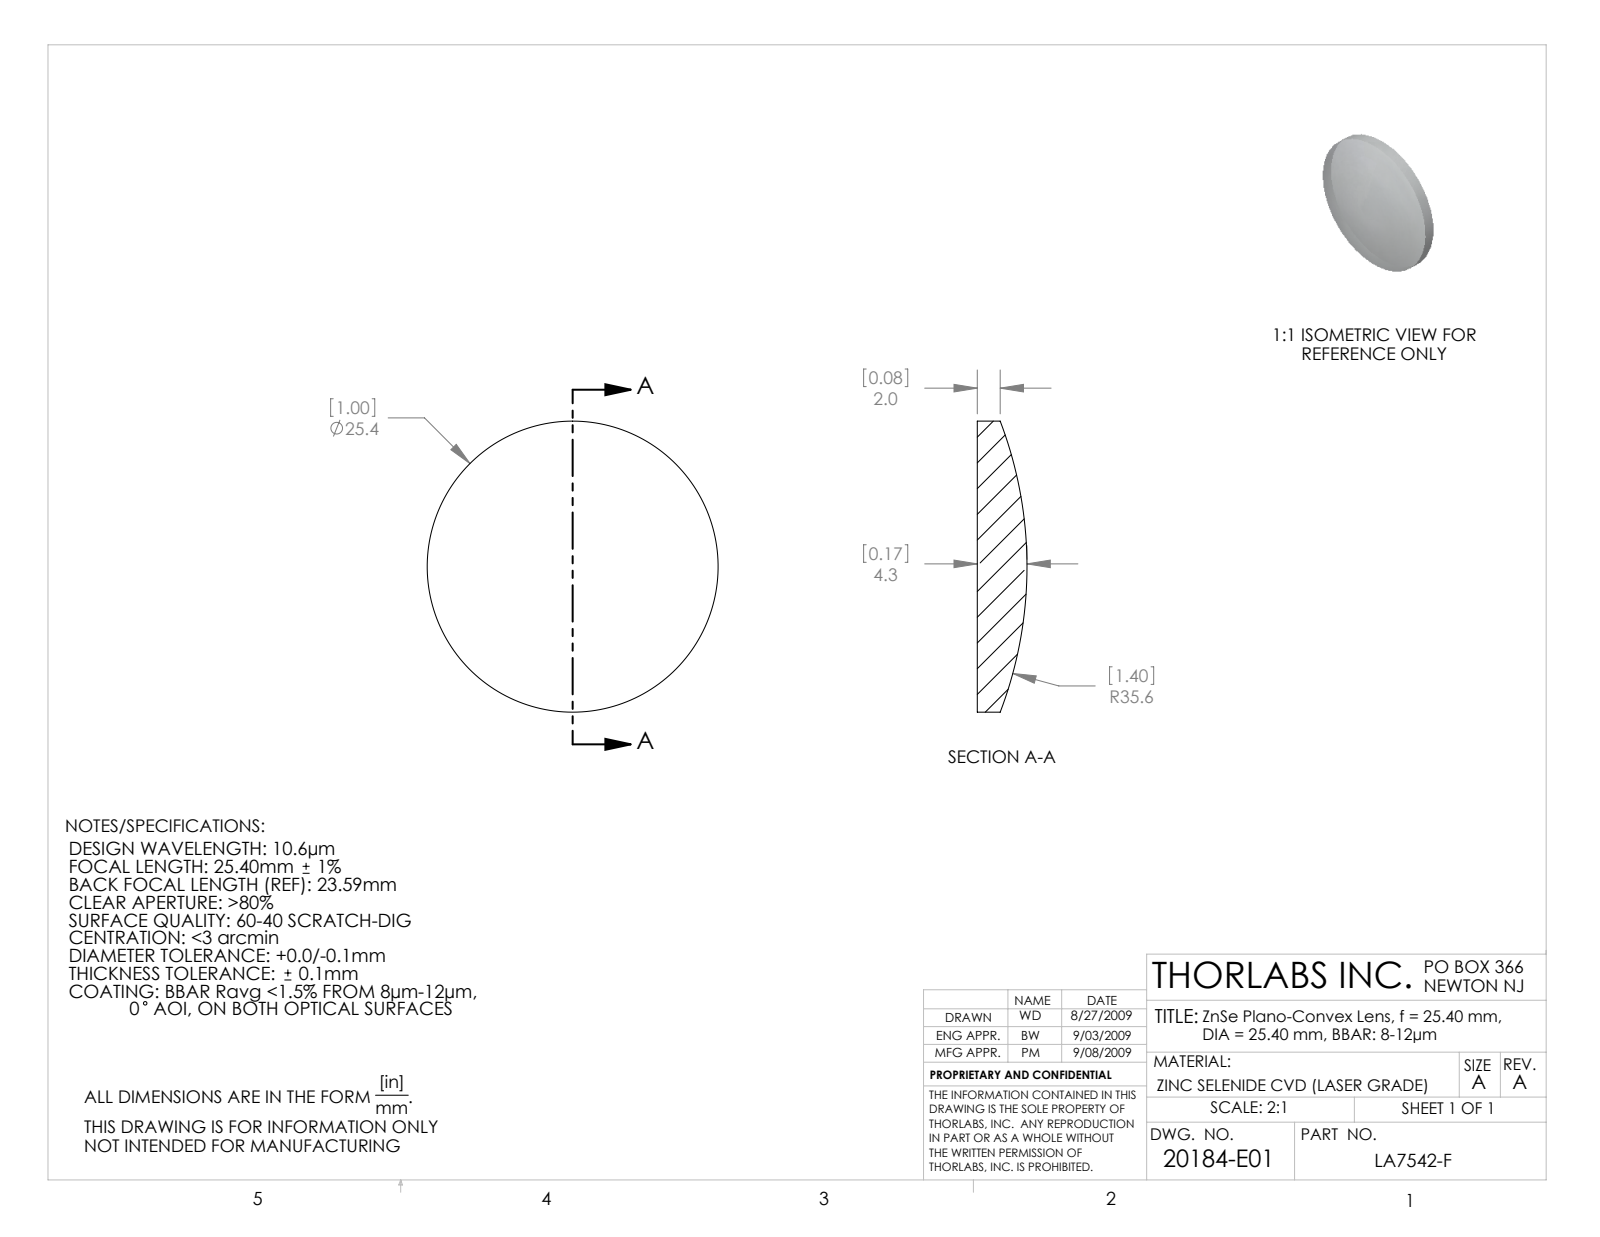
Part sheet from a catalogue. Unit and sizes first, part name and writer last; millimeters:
Units: millimetres
Overall size (bounding box): 25.4 × 25.4 × 4.34
Round bosses / shafts (diameter × count): ⌀25.4 ×1
Volume: 1 613 mm³ · Surface area: 1 190 mm²
Bodies: 1 solid, 5 faces (1 planar, 2 cylindrical, 2 other)
Part name (STEP PRODUCT): 20184-E0W
STEP written by: SolidWorks 2007 (CONFIG_CONTROL_DESIGN)
